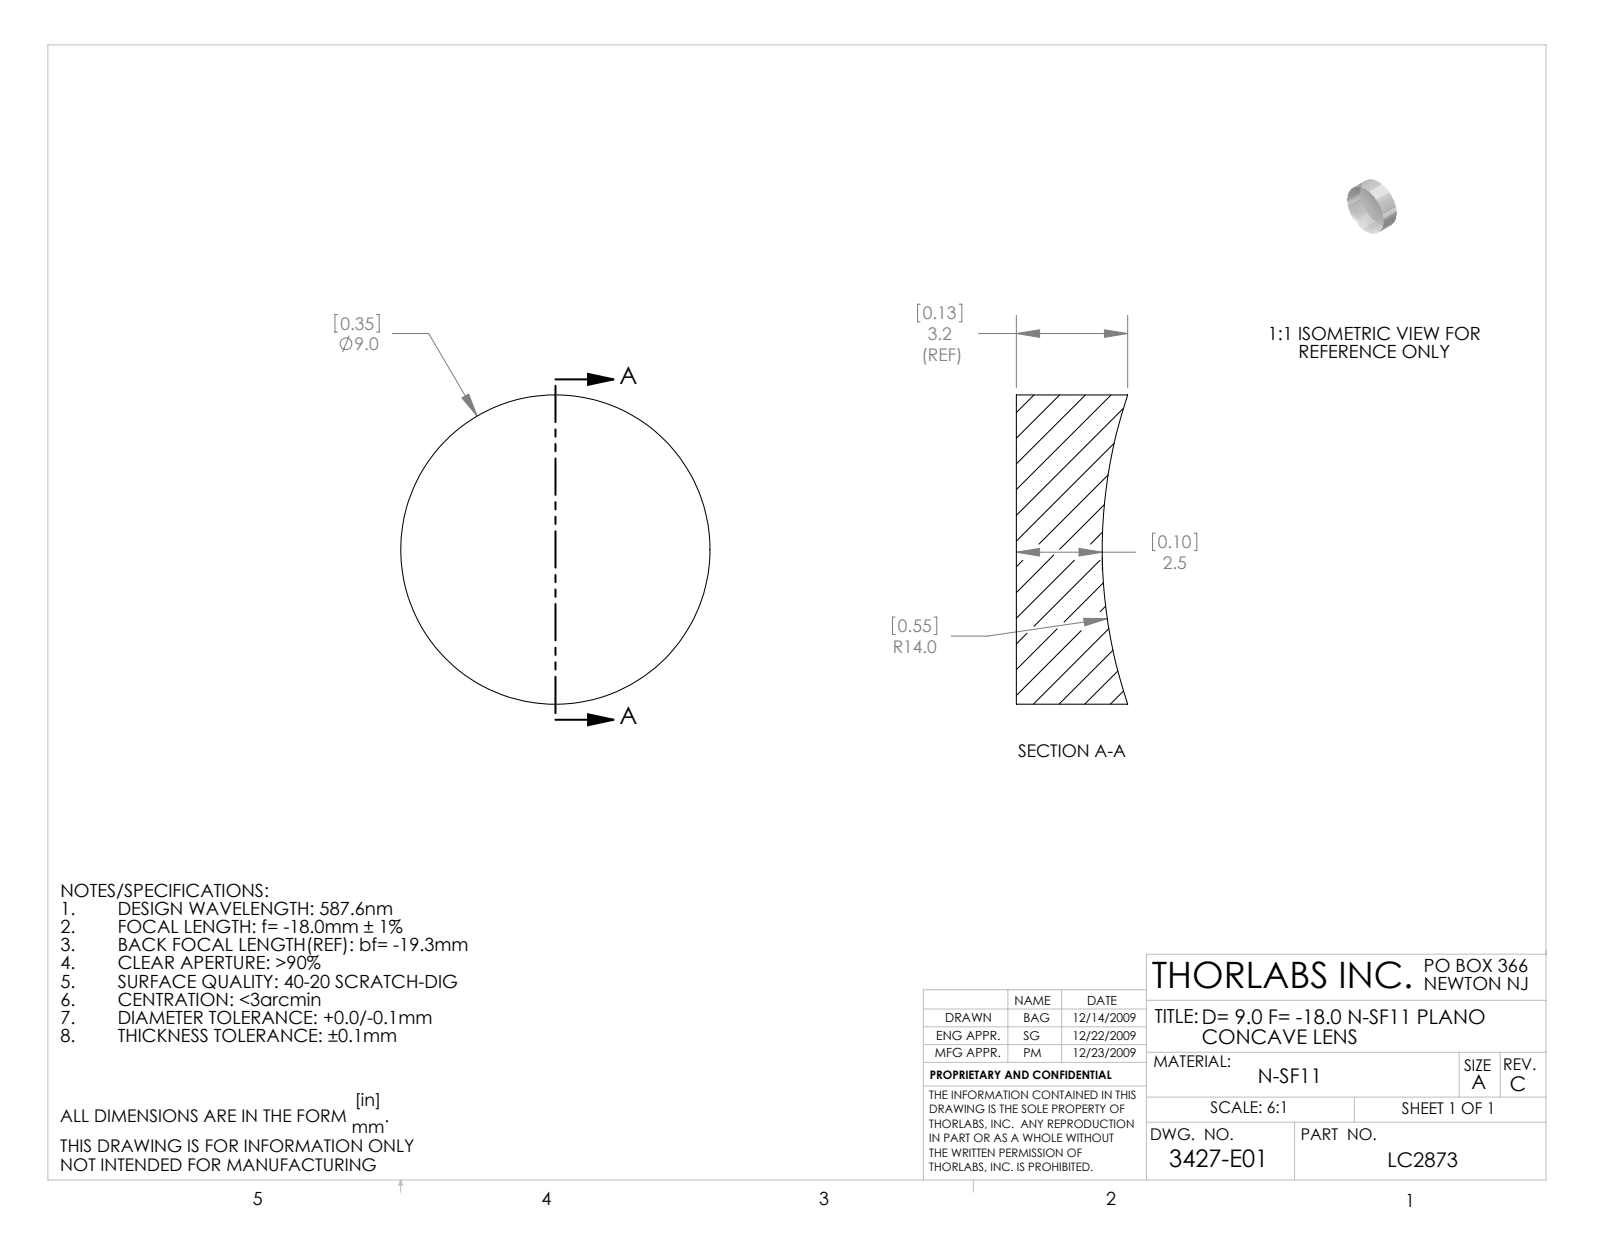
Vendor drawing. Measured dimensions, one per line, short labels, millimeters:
name: 3427-E0W
written by: SolidWorks 2009 (AUTOMOTIVE_DESIGN)
unit: mm
bodies: 1 solid, 5 faces (1 planar, 2 cylindrical, 2 other)
size: 9 × 9 × 3.3
volume: 180 mm³; area: 221 mm²
bosses: 1× ⌀9
